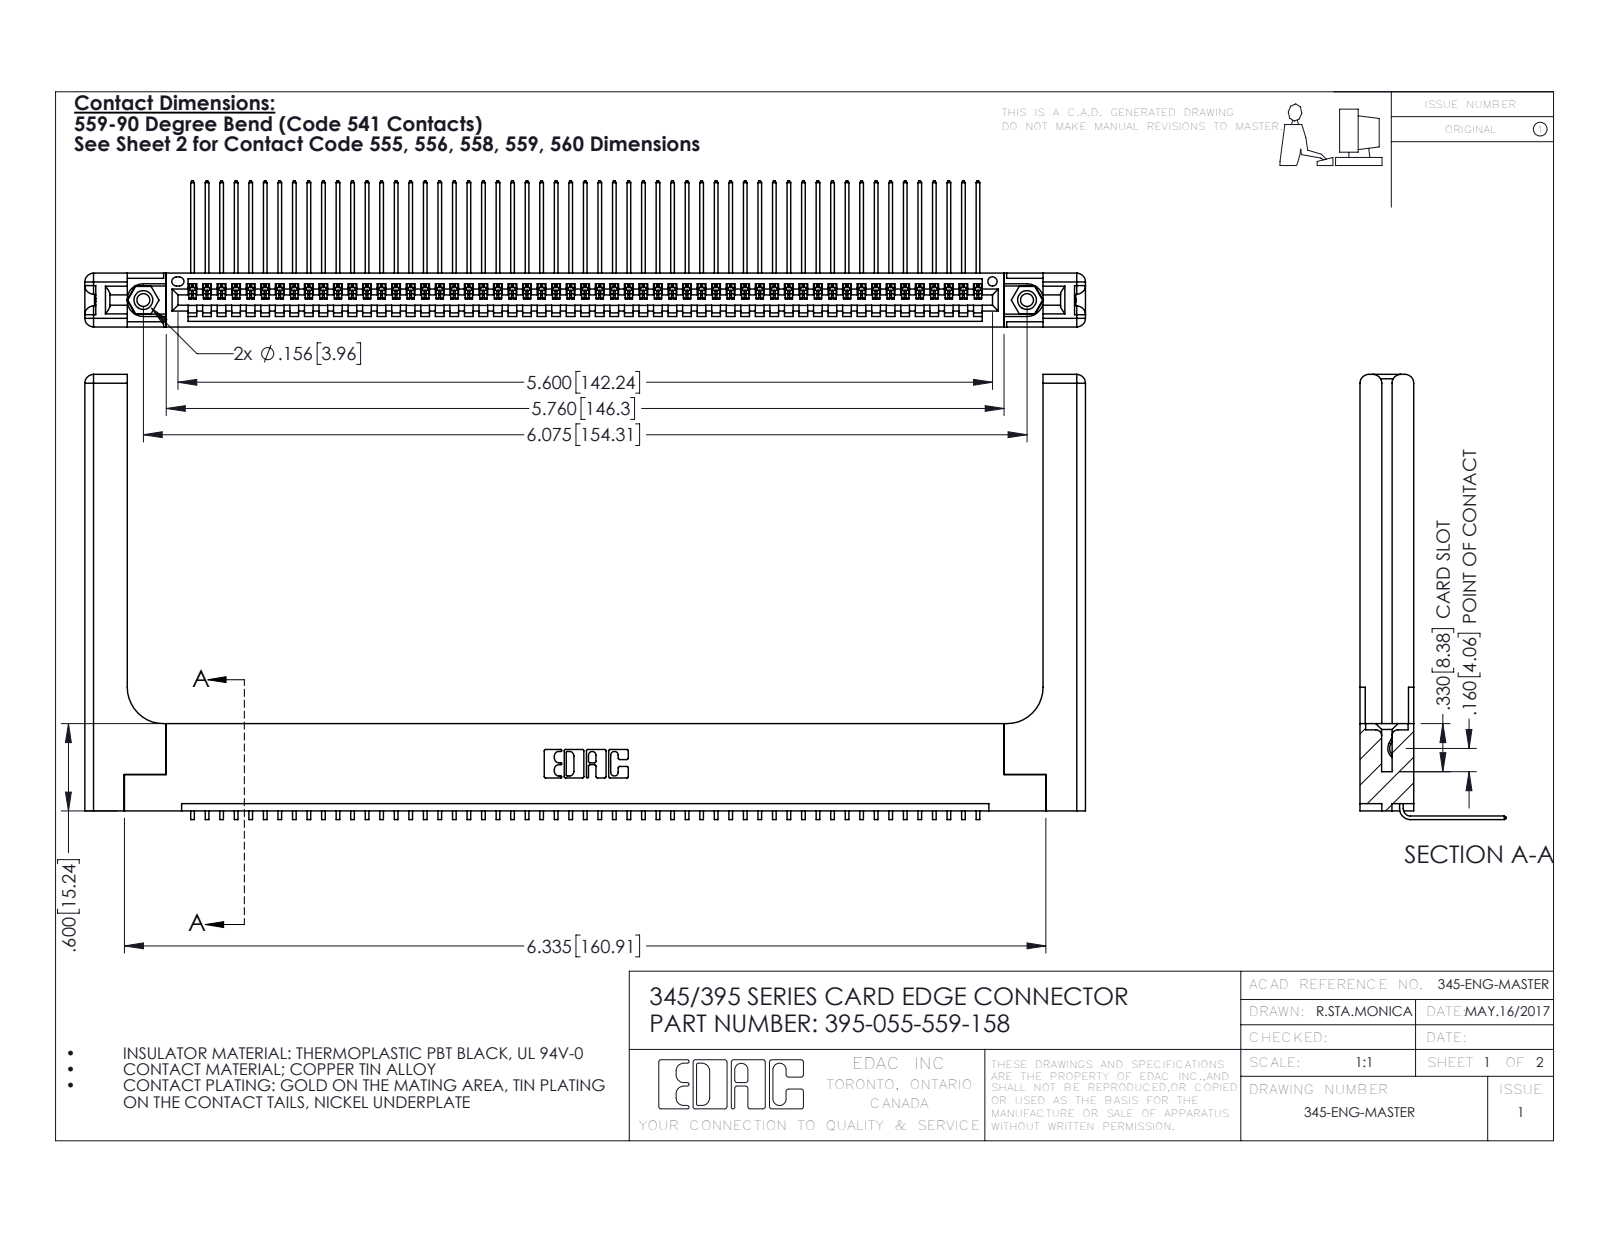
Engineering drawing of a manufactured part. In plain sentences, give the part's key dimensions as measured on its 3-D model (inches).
The part is named "345 Part_Flush Mounting Lugs - 0.156 Dia-TH; 345-220-058_345-220-058; 395-055-559-158; 345-292-001_558 559 Tail - 1 (+1 more)". Its 3-D file was written by "SolidWorks 2016 (CONFIG_CONTROL_DESIGN)". It is 60 solids with 3682 faces: 2538 planar, 1084 cylindrical and 60 other. Overall it measures 6.879 by 3.059 by 1.005 inches. Its volume is 1.549 cubic inches and its surface area 44.95 square inches. Round holes: 2 of diameter 0.089, 2 of diameter 0.125, 2 of diameter 0.156, 1 of diameter 0.064. Round bosses or shafts: 2 of diameter 0.155. Partial cylindrical surfaces (rounded edges, fillets, slot ends): 110 of radius 0.006, 22 of radius 0.01, 16 of radius 0.06, 6 of radius 0.007, 6 of radius 0.031, 3 of radius 0.026, 2 of radius 0.03, 2 of radius 0.031. The main face-to-face distances are 0.072, 0.37, 0.298, 0.2, 0.098, 0.272, 0.025, 0.225, 0.148, 0.15. The hole center spacings are 0.27, 5.839, 6.075.
